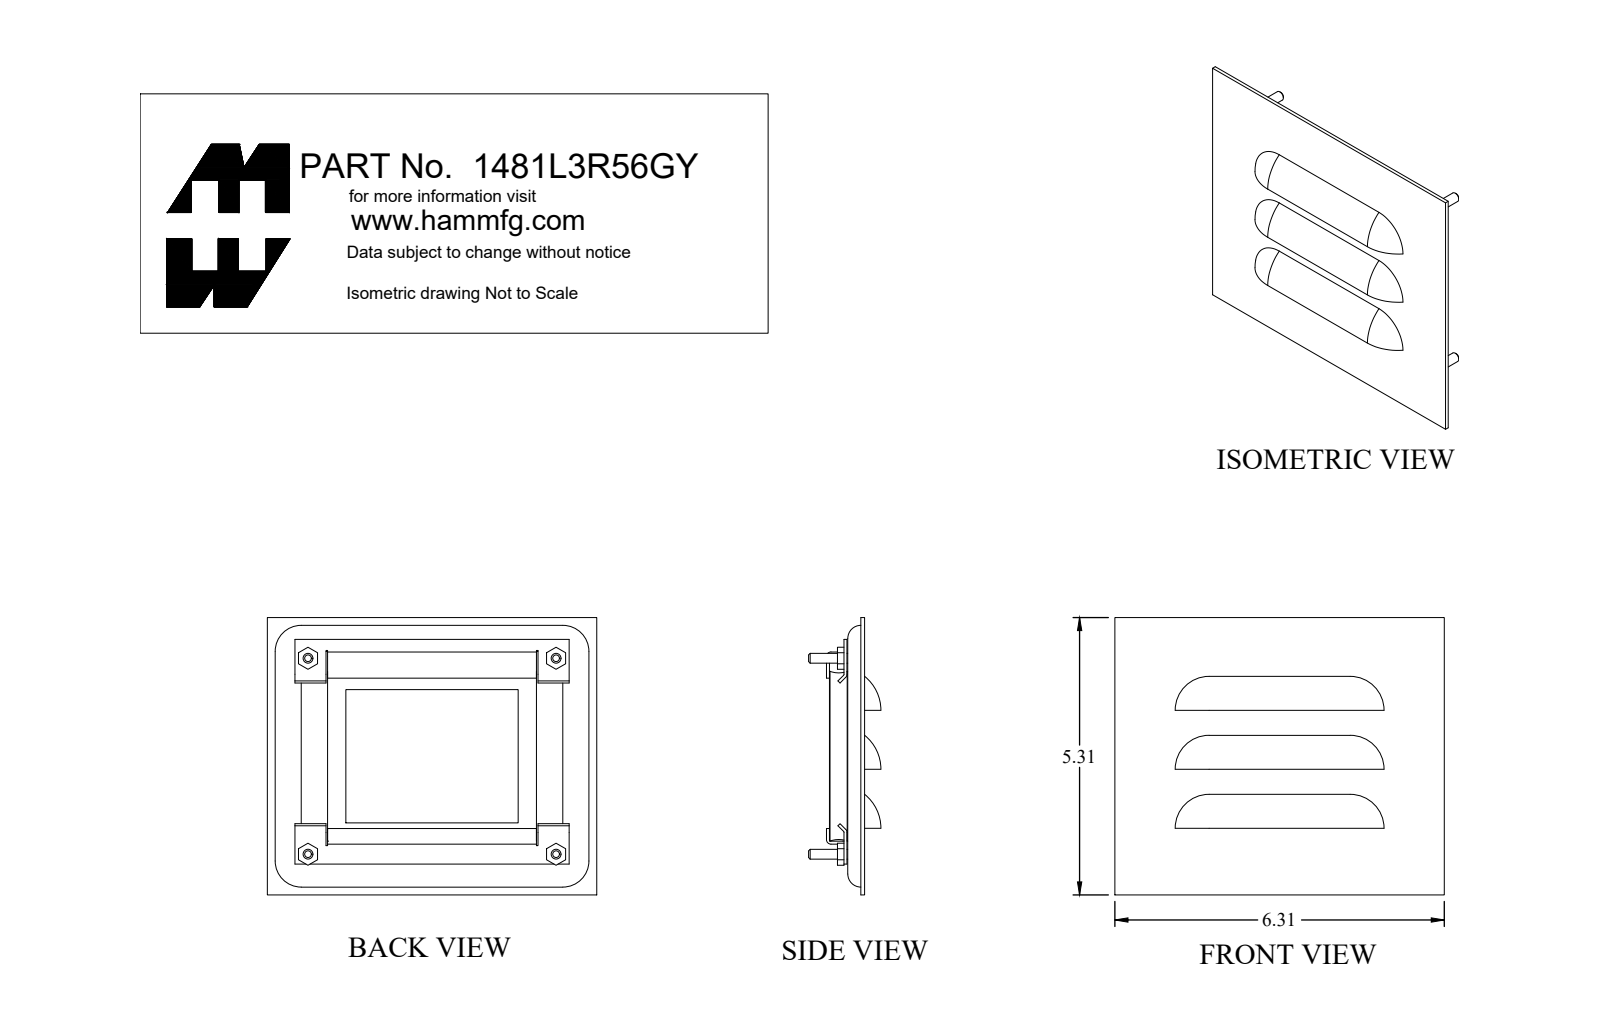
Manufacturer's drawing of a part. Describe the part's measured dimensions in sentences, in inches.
The part is named "1481L3R56GY_Default". Its 3-D file was written by "SolidWorks 2019 (CONFIG_CONTROL_DESIGN)". It is 13 solids with 240 faces: 138 planar, 70 cylindrical and 32 other. Overall it measures 6.308 by 5.308 by 1.384 inches. Its volume is 8.741 cubic inches and its surface area 175.8 square inches. Round holes: 4 of diameter 0.156, 4 of diameter 0.205. Round bosses or shafts: 4 of diameter 0.25, 4 of diameter 0.188. Partial cylindrical surfaces (rounded edges, fillets, slot ends): 6 of radius 0.029, 6 of radius 0.086, 4 of radius 0.25, 4 of radius 0.469, 4 of radius 0.499, 3 of radius 0.761, 3 of radius 0.833. The main face-to-face distances are 0.072, 0.3, 0.25, 0.05, 0.073, 0.322, 0.372, 0.622, 0.55, 0.299. The hole center spacings are 3.75, 4.75, 4.75, 6.051, 6.052.
